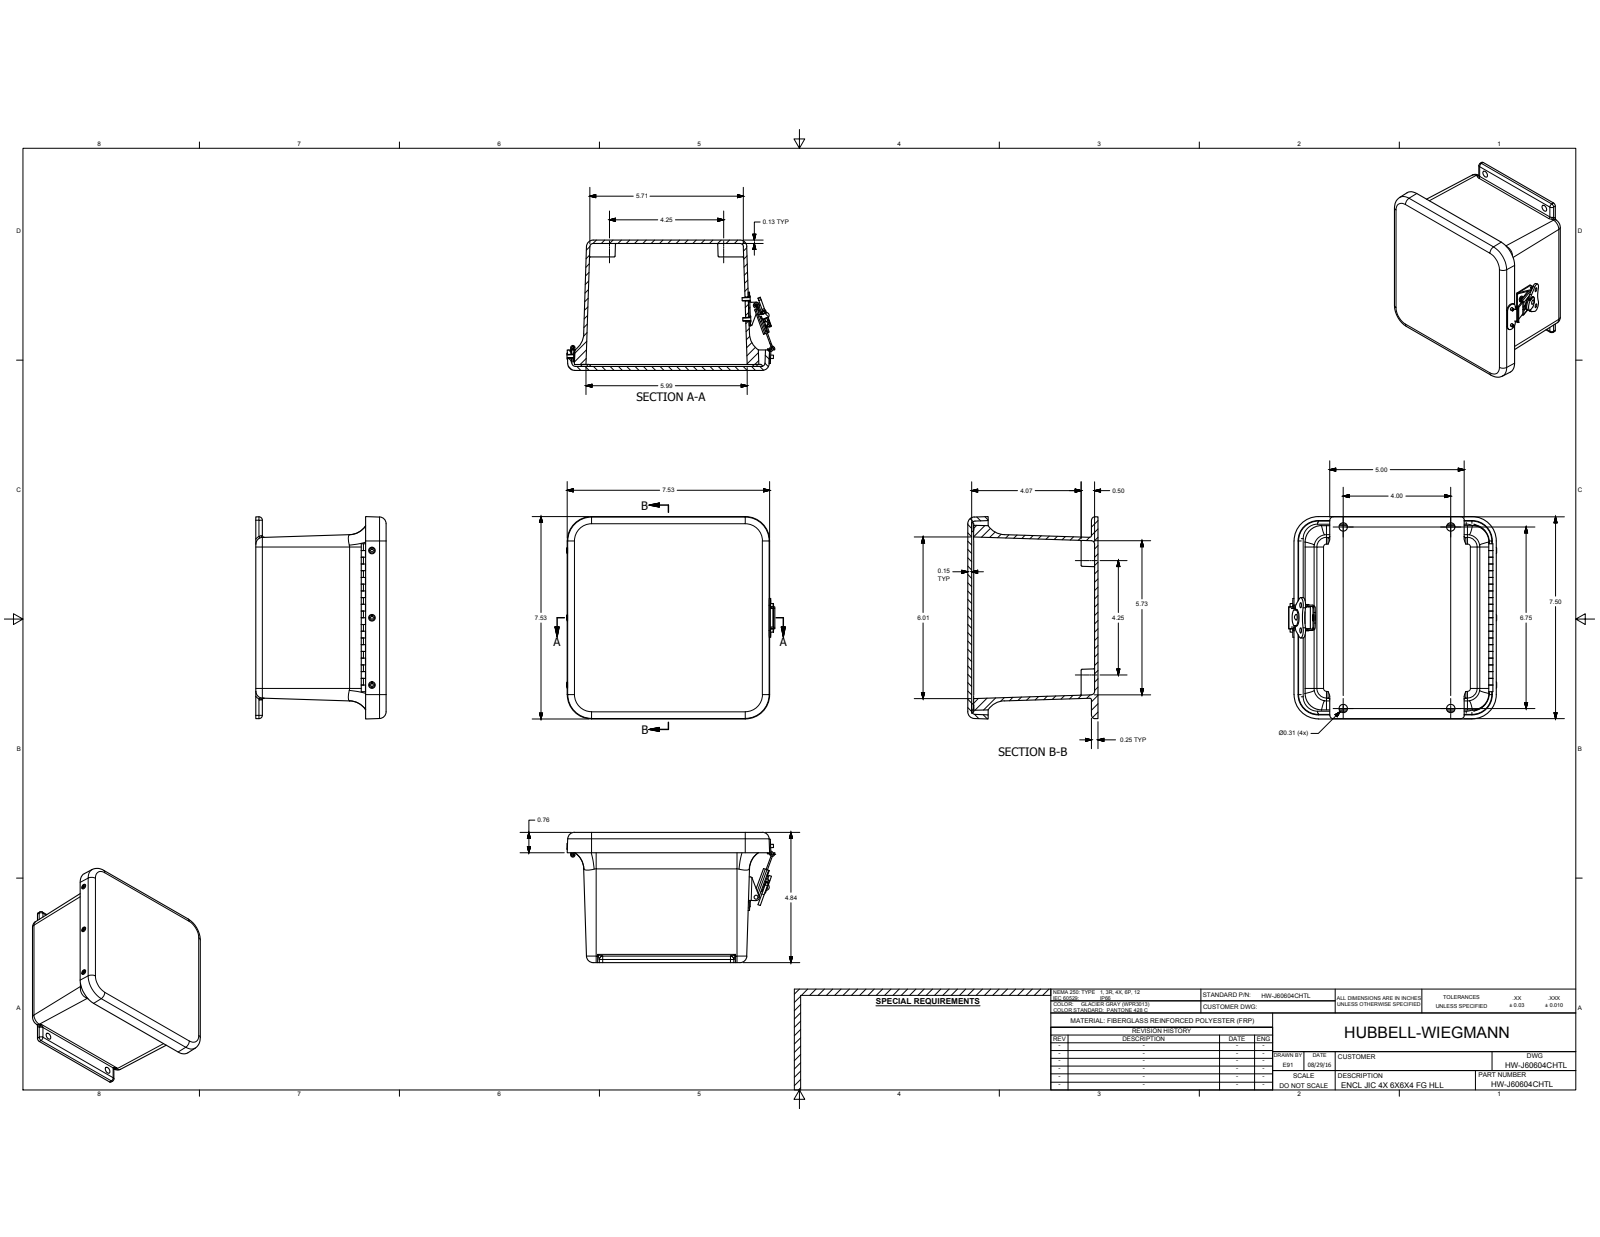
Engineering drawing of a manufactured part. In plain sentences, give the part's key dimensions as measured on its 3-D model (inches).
The part is named "HW-J606CHTL; WP606H&LBOX; WP606HLU; WP606HCVR (+8 more)". Its 3-D file was written by "Autodesk Inventor 2017 (CONFIG_CONTROL_DESIGN)". It is 29 solids with 768 faces: 289 planar, 307 cylindrical and 172 other. Overall it measures 7.809 by 7.525 by 4.838 inches. Its volume is 37.25 cubic inches and its surface area 519.2 square inches. Round holes: 10 of diameter 0.14, 9 of diameter 0.104, 8 of diameter 0.152, 5 of diameter 0.131, 4 of diameter 0.159, 4 of diameter 0.218, 4 of diameter 0.312, 2 of diameter 0.13, 2 of diameter 0.133, 2 of diameter 0.187, 1 of diameter 0.067, 1 of diameter 0.085. Round bosses or shafts: 9 of diameter 0.125, 4 of diameter 0.27, 1 of diameter 0.66, 1 of diameter 0.582, 1 of diameter 0.525, 1 of diameter 0.286, 1 of diameter 0.213, 1 of diameter 0.18. Partial cylindrical surfaces (rounded edges, fillets, slot ends): 36 of radius 0.031, 17 of radius 0.125, 9 of radius 0.25, 8 of radius 0.015, 8 of radius 0.074, 7 of radius 0.06, 4 of radius 0.011, 4 of radius 0.02. The main face-to-face distances are 0.147, 4.691, 4.838, 0.125, 4.566, 4.713, 0.152, 4.5, 4.625, 0.066. The hole center spacings are 5.308, 2.5, 4.25, 4.31, 4, 4.25, 1.256, 5.
